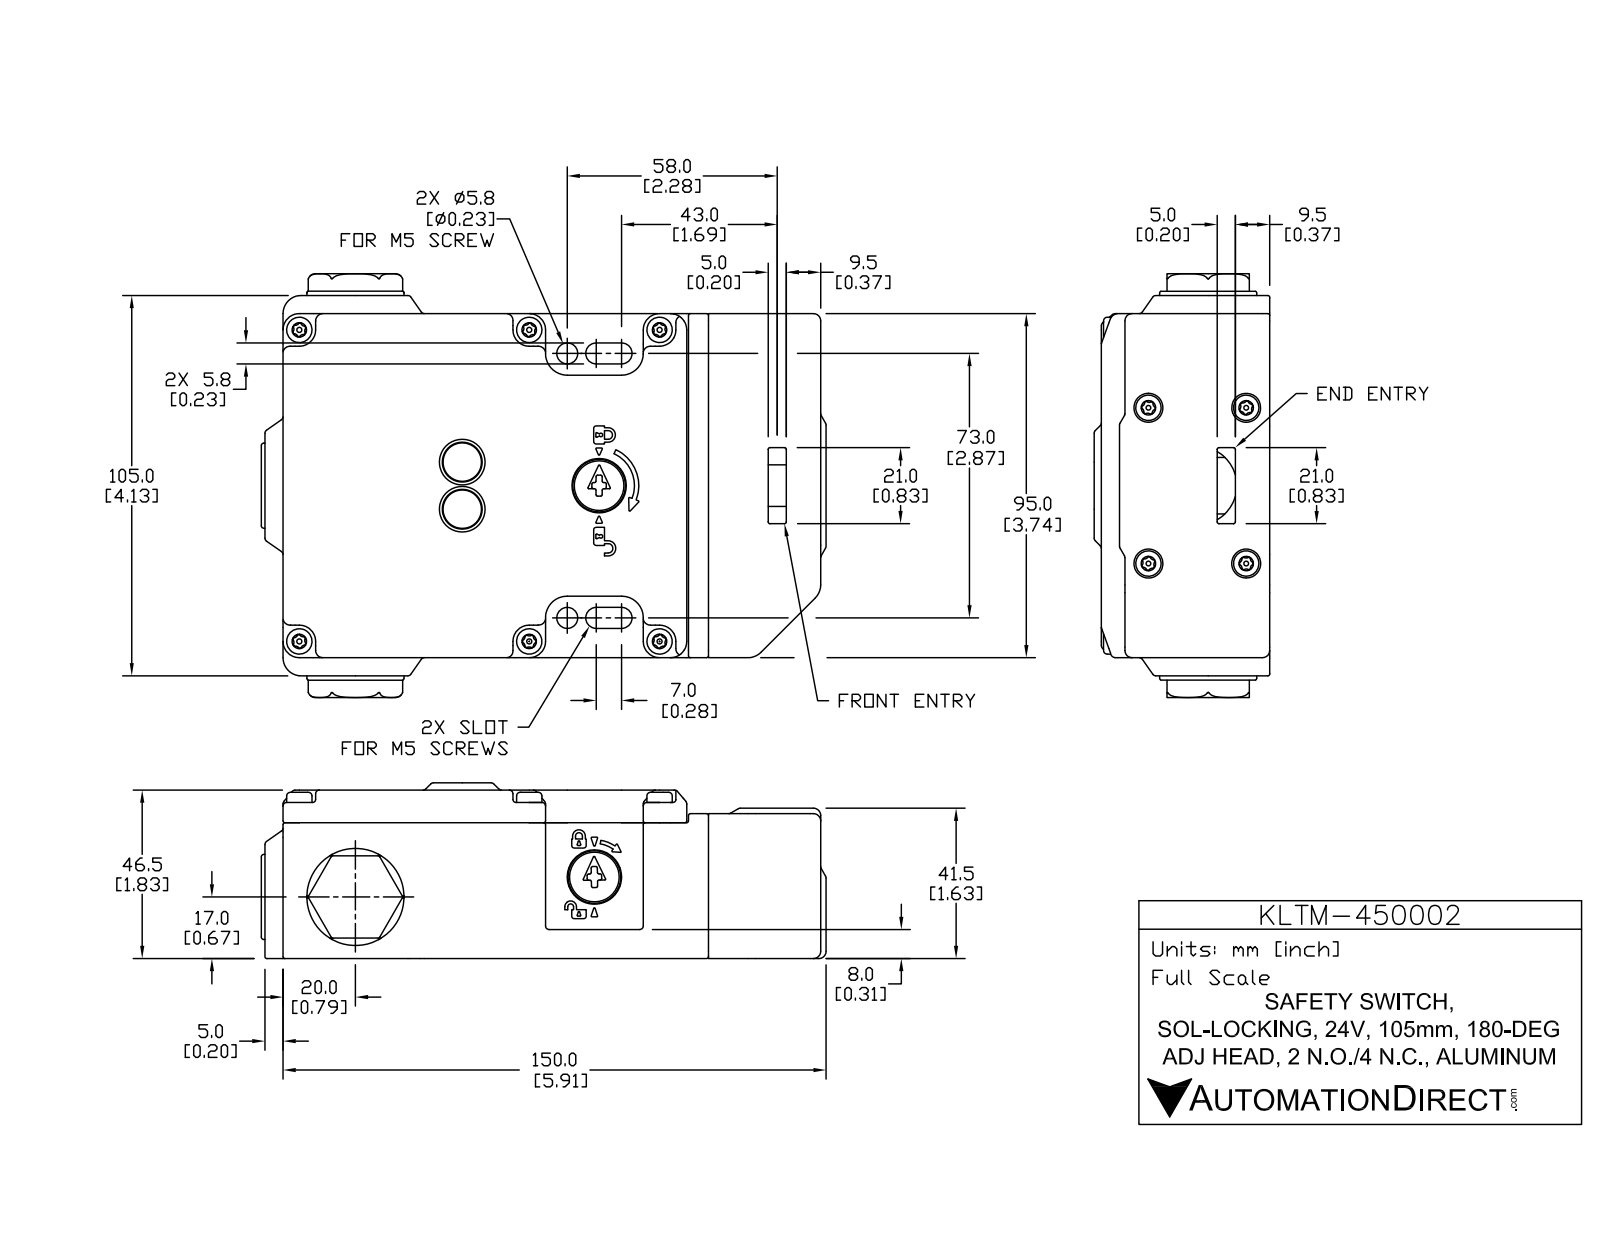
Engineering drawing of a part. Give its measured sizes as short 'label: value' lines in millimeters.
name: KLTM-450002
written by: SolidWorks 2017 (AUTOMOTIVE_DESIGN)
unit: mm
bodies: 23 solids, 4546 faces (1096 planar, 1816 cylindrical, 1634 other)
size: 156 × 117 × 48.5
volume: 210 600 mm³; area: 137 800 mm²
holes: 10× ⌀3.3, 10× ⌀4, 8× ⌀2.5, 8× ⌀8, 6× ⌀4.1, 6× ⌀4.5, 6× ⌀4.6, 4× ⌀4.2, 4× ⌀5, 2× ⌀2.2, 2× ⌀5.5, 2× ⌀5.8
bosses: 10× ⌀7, 10× ⌀3.5, 6× ⌀5.6, 6× ⌀1.4, 5× ⌀6, 4× ⌀1.3, 3× ⌀7.8, 2× ⌀18
rounds: 491× R0.5, 222× R1, 104× R0.3, 80× R0.2, 32× R0.4, 21× R2, 16× R0.7, 14× R0.2
face distances: 3, 2.2, 46.5, 44.3, 2.5, 3.2, 3.5, 6.5, 6, 34.5
hole spacings: 25.4, 62.8, 86, 4.7, 9.7, 10.1, 10.2, 10.5
